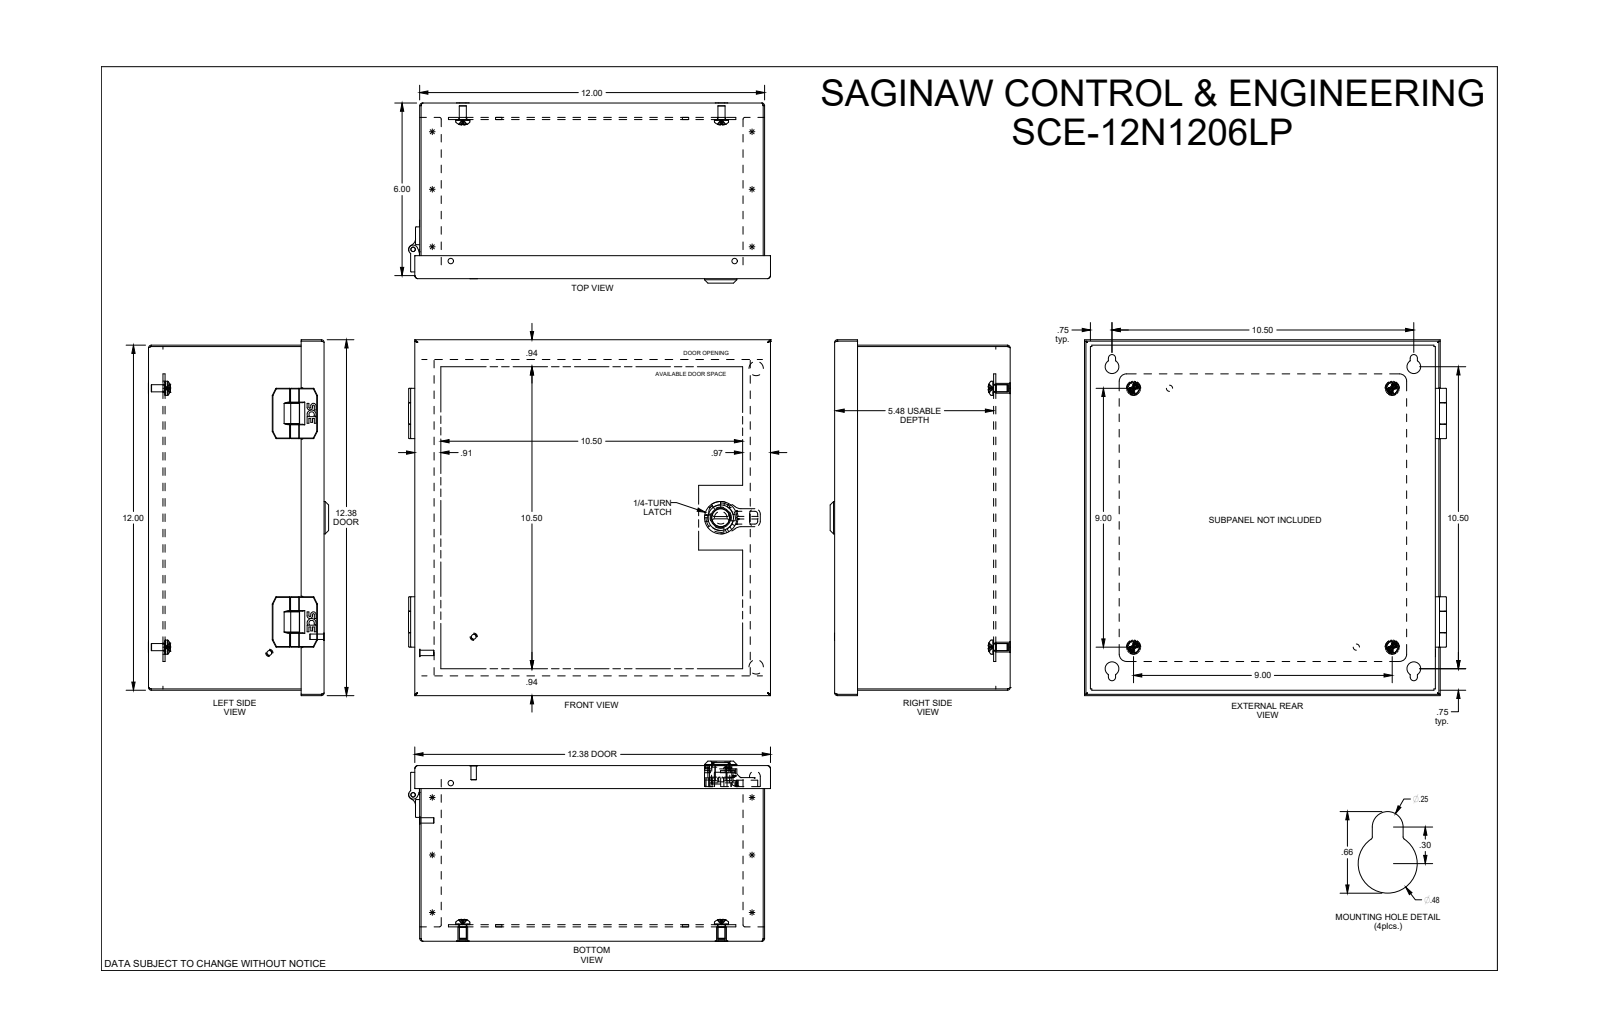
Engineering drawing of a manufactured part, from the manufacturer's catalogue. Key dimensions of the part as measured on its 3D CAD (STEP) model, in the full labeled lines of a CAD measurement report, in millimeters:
Part name (STEP PRODUCT): SCE-12N1206LP
STEP written by: SolidWorks 2019 (AUTOMOTIVE_DESIGN)
Units: millimetres
Bodies: 31 solids, 1545 faces (578 planar, 643 cylindrical, 324 other)
Overall size (bounding box): 319.9 × 314.3 × 159.2
Volume: 778 500 mm³ · Surface area: 982 600 mm²
Round holes (diameter × count): ⌀4.3 ×4, ⌀6.4 ×4, ⌀7.1 ×4, ⌀8.4 ×4, ⌀8.7 ×4, ⌀12.2 ×4, ⌀4.9 ×3, ⌀4.7 ×2, ⌀5.5 ×2, ⌀4 ×1, ⌀11.2 ×1, ⌀16.1 ×1
Round bosses / shafts (diameter × count): ⌀12.5 ×4, ⌀12.2 ×4, ⌀8.7 ×4, ⌀6.3 ×4, ⌀6 ×4, ⌀4.1 ×4, ⌀12.7 ×2, ⌀8.2 ×2
Partial cylindrical surfaces — rounded edges, fillets, slot ends (radius × count): R0.3 ×253, R0.5 ×95, R1.5 ×25, R0.4 ×24, R0.6 ×24, R1.4 ×6, R6.4 ×6, R3.2 ×4
Main face-to-face distances: 1.5, 153.6, 303.3, 152.1, 155.1, 304.8, 301.8, 12.7, 11.2, 14.6
Hole centre spacings: 248.4, 26.9, 196.9, 228.6, 266.7, 350.2, 27.7, 27.7
